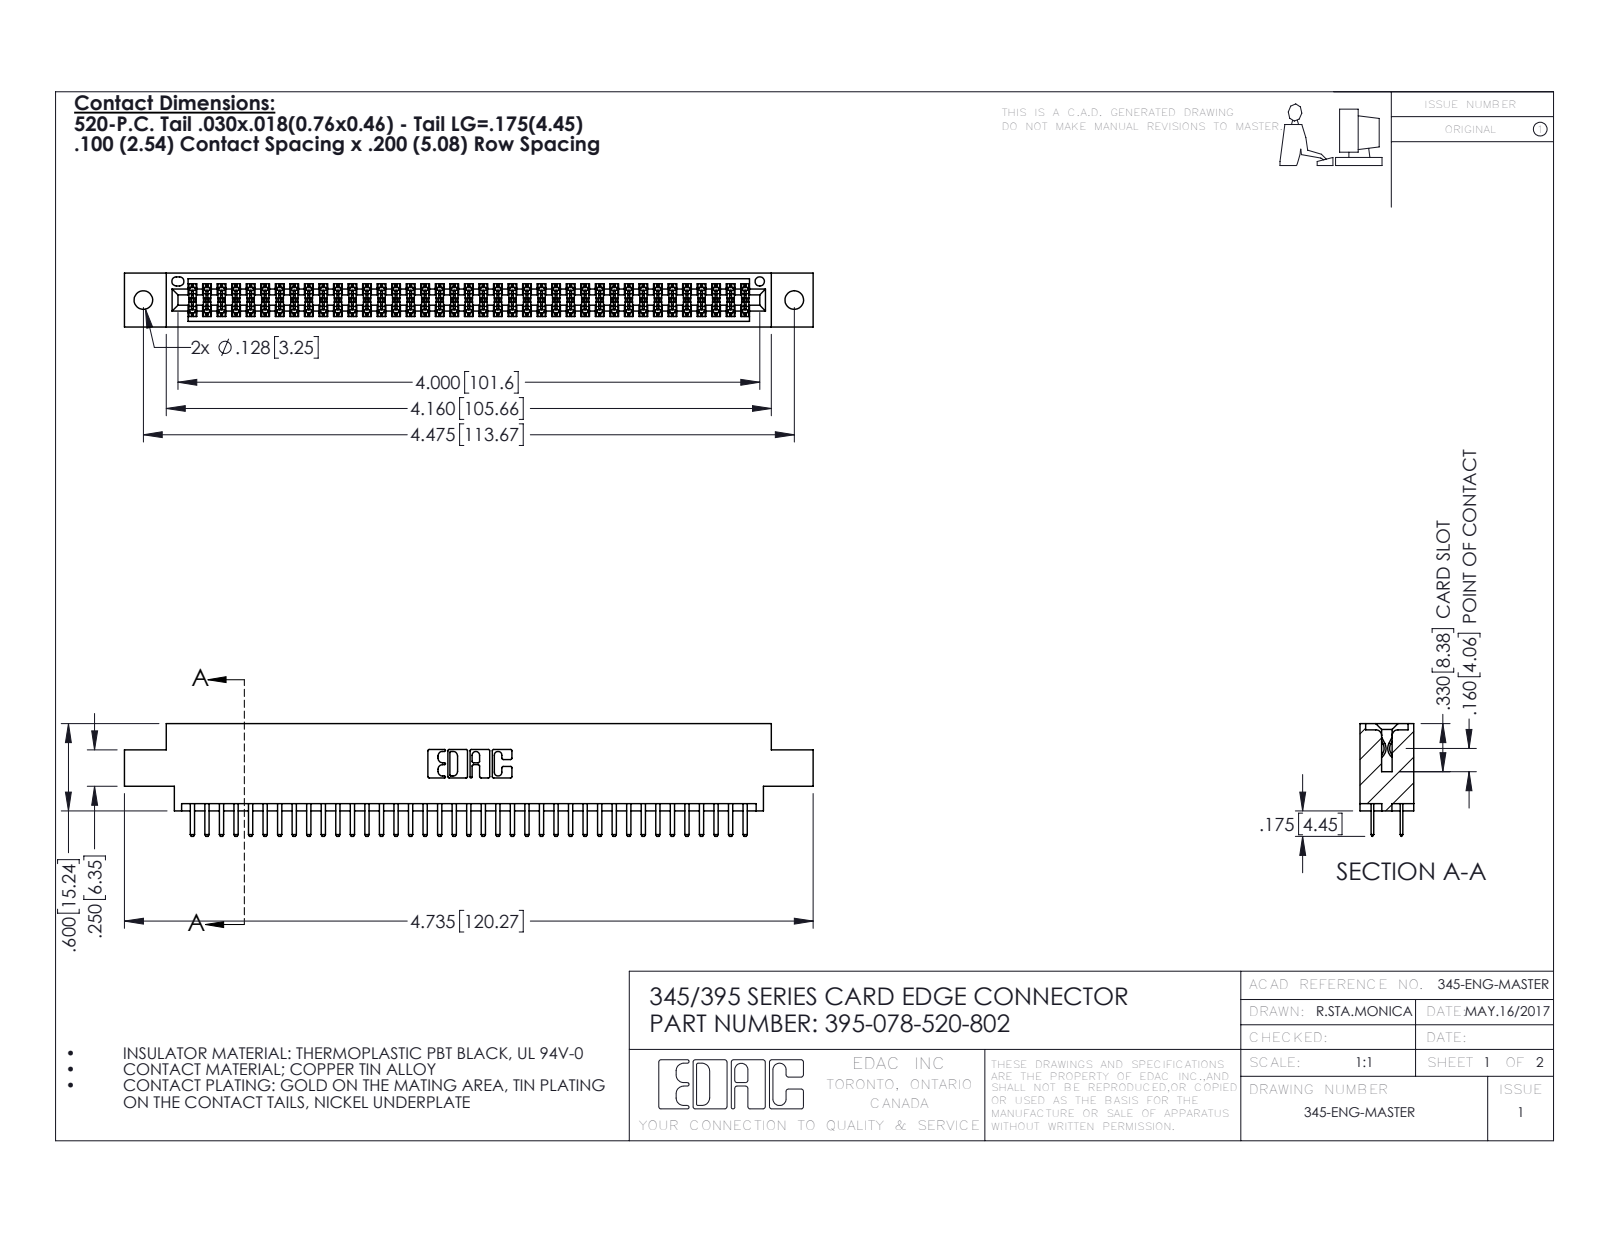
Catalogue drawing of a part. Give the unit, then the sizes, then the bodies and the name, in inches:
Units: inches
Overall size (bounding box): 4.735 × 0.775 × 0.37
Round holes (diameter × count): ⌀0.128 ×2, ⌀0.064 ×1
Partial cylindrical surfaces — rounded edges, fillets, slot ends (radius × count): R0.006 ×117, R0.01 ×82, R0.01 ×22, R0.007 ×6, R0.031 ×6, R0.026 ×3, R0.014 ×2, R0.019 ×2
Main face-to-face distances: 0.298, 0.072, 0.2, 0.37, 0.098, 0.272, 0.025, 0.225, 0.022, 0.175
Hole centre spacings: 0.27, 4.239, 4.475
Volume: 0.7 in³ · Surface area: 25.88 in²
Bodies: 79 solids, 4342 faces (2814 planar, 1528 cylindrical, 0 other)
Part name (STEP PRODUCT): 345-292-001_345-293-120; 345 Part_0.170 Offset - 0.128 Dia; 395-078-520-802
STEP written by: SolidWorks 2016 (CONFIG_CONTROL_DESIGN)
